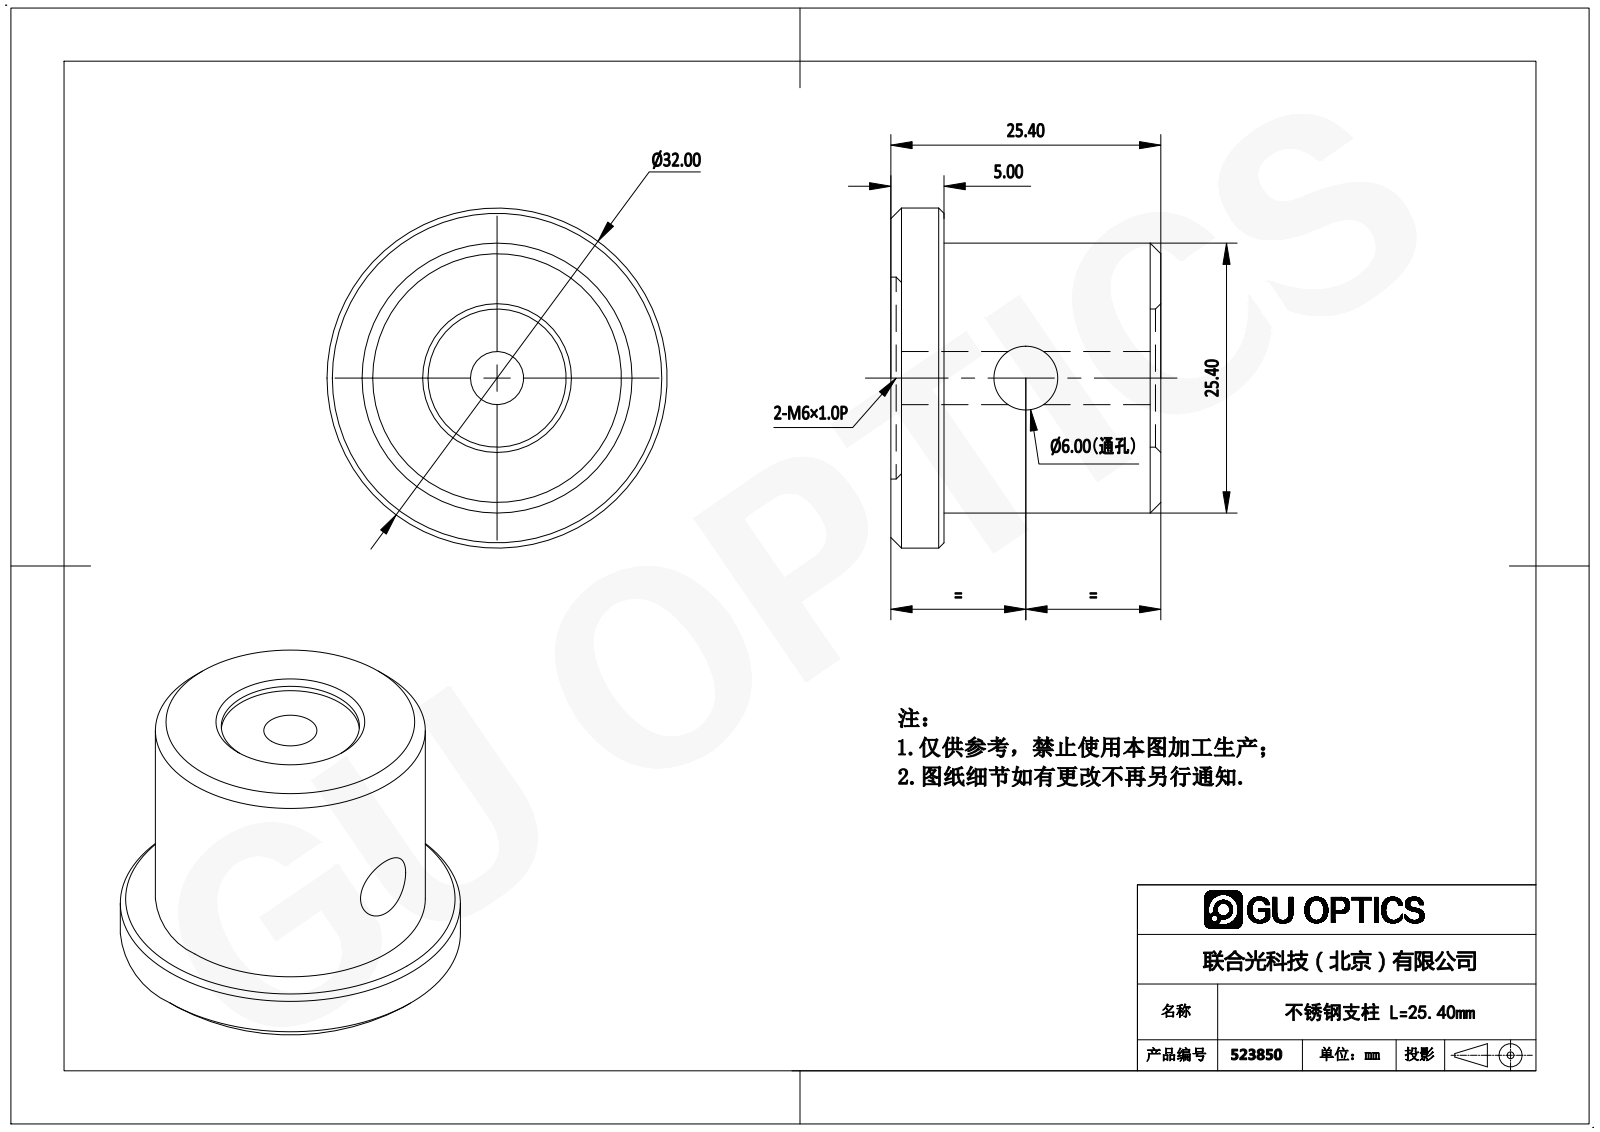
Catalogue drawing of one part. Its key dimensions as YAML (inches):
part_name: "523850"
step_written_by: "SolidWorks 2016 (AUTOMOTIVE_DESIGN)"
units: inches
bodies: {solids: 1, faces: 29, planar: 5, cylindrical: 14, other: 10}
overall_size: [1.26, 1.26, 1]
volume: 0.78
surface_area: 6.66
round_holes:
  - {diameter: 0.197, count: 1}
  - {diameter: 0.236, count: 1}
  - {diameter: 0.512, count: 1}
  - {diameter: 0.748, count: 1}
round_bosses_or_shafts:
  - {diameter: 1.26, count: 1}
  - {diameter: 1, count: 1}
face_to_face_distances: [0.039, 0.961, 1, 0.197, 0.803, 0.157, 0.921, 0.764]
